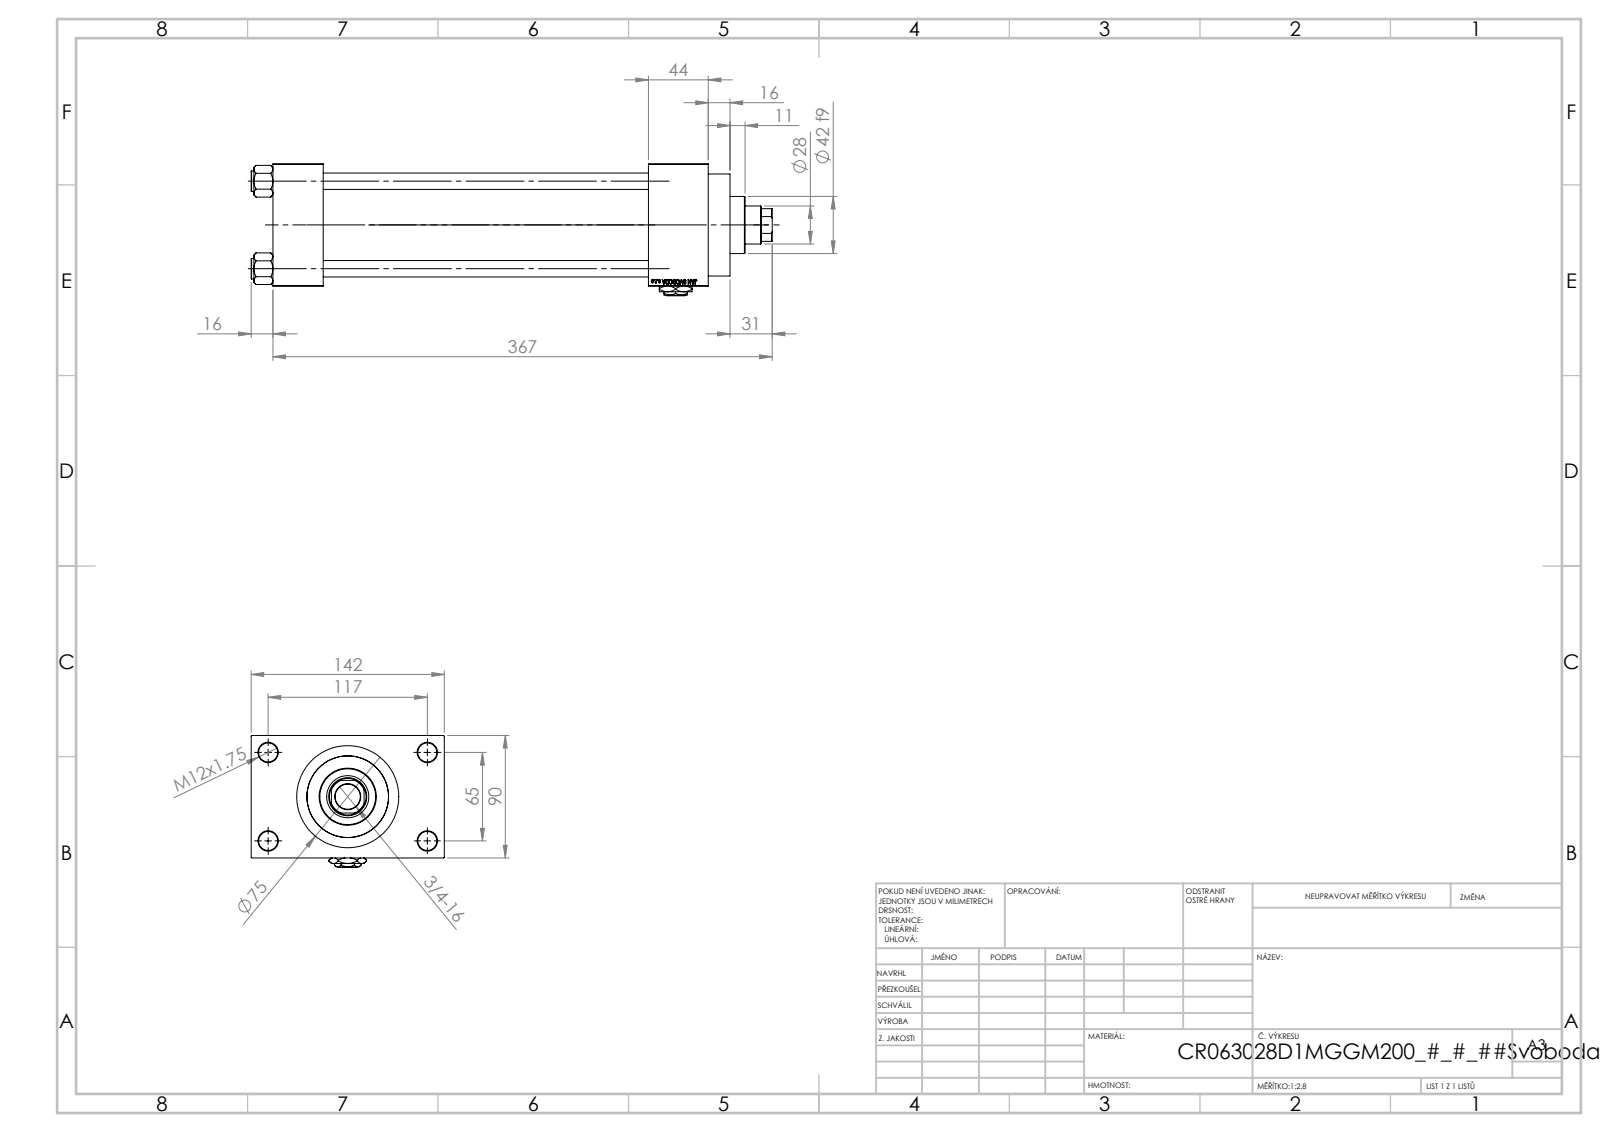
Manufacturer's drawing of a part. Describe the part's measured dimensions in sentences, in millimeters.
The part is named "V215_VC_A; V215CR_VCP_D; V215CR_D_Body; V215CR_D_TYCINKA (+2 more)". Its 3-D file was written by "SolidWorks 2019 (CONFIG_CONTROL_DESIGN)". It is 12 solids with 1152 faces: 521 planar, 93 cylindrical and 538 other. Overall it measures 383 by 142 by 97 millimeters. Its volume is 1 406 000 cubic millimeters and its surface area 318 085 square millimeters. Round holes: 4 of diameter 12, 4 of diameter 14, 2 of diameter 7, 2 of diameter 20.96, 2 of diameter 30, 1 of diameter 18.5, 1 of diameter 28, 1 of diameter 31, 1 of diameter 50, 1 of diameter 60, 1 of diameter 63. Round bosses or shafts: 4 of diameter 15, 1 of diameter 75, 1 of diameter 69, 1 of diameter 42. Partial cylindrical surfaces (rounded edges, fillets, slot ends): 1 of radius 13.5. The main face-to-face distances are 90, 239, 37, 276, 283, 320, 44, 26, 116, 142. The hole center spacings are 26.35, 45.47, 64.3, 66.92, 69.81, 90.65, 111.34, 65.
